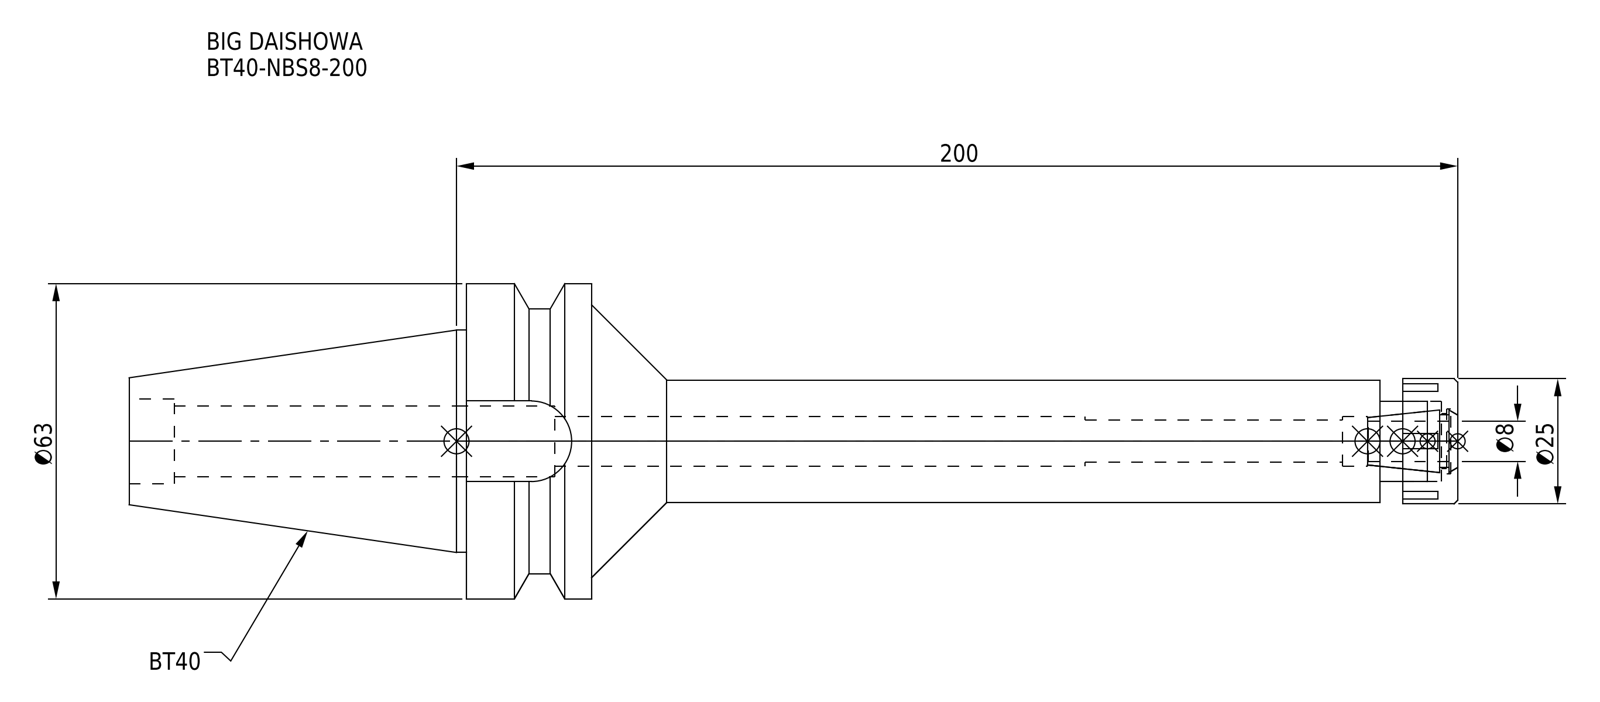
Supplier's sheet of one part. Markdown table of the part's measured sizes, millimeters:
| quantity | value |
| --- | --- |
| part name | BT40-NBS8-200-FreeParts; BT40-NBS8-200_1.stp; BT40NB08200-080_ASM.stp; BT40-NBS8-200 (+3 more) |
| STEP written by | SolidWorks 2019 (CONFIG_CONTROL_DESIGN) |
| units | millimeters |
| bodies | 2 solids, 93 faces (45 planar, 34 cylindrical, 14 other) |
| overall size | 265.4 × 63 × 63 |
| volume | 199 195 mm³ |
| surface area | 42 244 mm² |
| round holes (diameter × count) | 8.4 × 1, 10 × 1, 11 × 1, 13 × 1, 14.2 × 1, 16 × 1, 17 × 1 |
| round bosses / shafts (diameter × count) | 63 × 1, 53 × 1, 44.45 × 1, 25 × 1, 24.5 × 1 |
| partial cylindrical surfaces (radius × count) | 8.05 × 1 |
| main face-to-face distances | 25, 173, 198, 45, 265.4, 92.4, 67.4, 15.5, 157.5, 182.5 |
